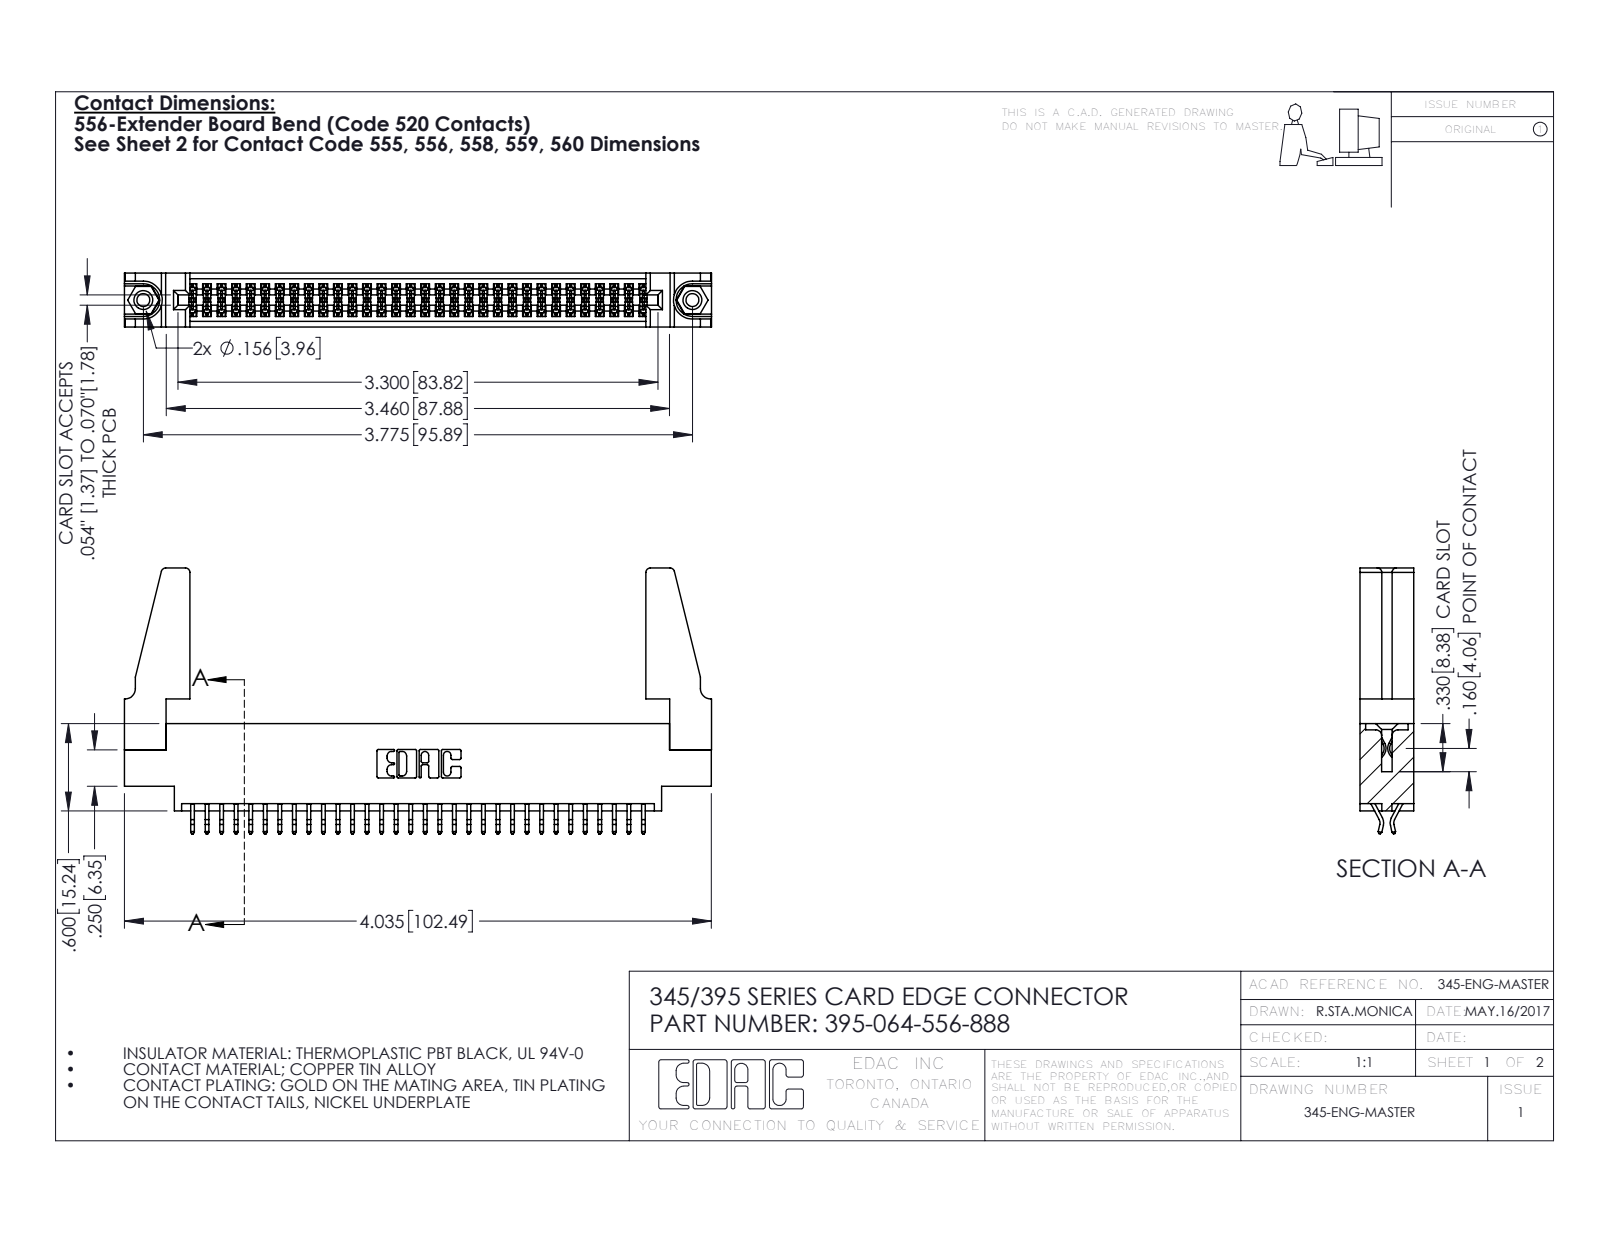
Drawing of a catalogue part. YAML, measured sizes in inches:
part_name: "395-064-556-888; 345-220-078_345-220-088; 345-250-001_345-250-001-102; 345 Part_0.170 Offset - 0.156 Dia-TH (+1 more)"
step_written_by: "SolidWorks 2016 (CONFIG_CONTROL_DESIGN)"
units: inches
bodies: {solids: 69, faces: 3838, planar: 2524, cylindrical: 1298, other: 16}
overall_size: [4.036, 1.827, 0.37]
volume: 0.793
surface_area: 27.01
round_holes:
  - {diameter: 0.089, count: 2}
  - {diameter: 0.125, count: 2}
  - {diameter: 0.156, count: 2}
  - {diameter: 0.064, count: 1}
round_bosses_or_shafts:
  - {diameter: 0.155, count: 2}
partial_cylinders:
  - {radius: 0.006, count: 96}
  - {radius: 0.01, count: 22}
  - {radius: 0.03, count: 8}
  - {radius: 0.007, count: 6}
  - {radius: 0.031, count: 6}
  - {radius: 0.026, count: 3}
  - {radius: 0.01, count: 2}
  - {radius: 0.014, count: 2}
face_to_face_distances: [0.072, 0.37, 0.298, 0.025, 0.2, 0.098, 0.272, 0.225, 0.175, 0.149]
hole_center_spacings: [0.27, 3.54, 3.775]
